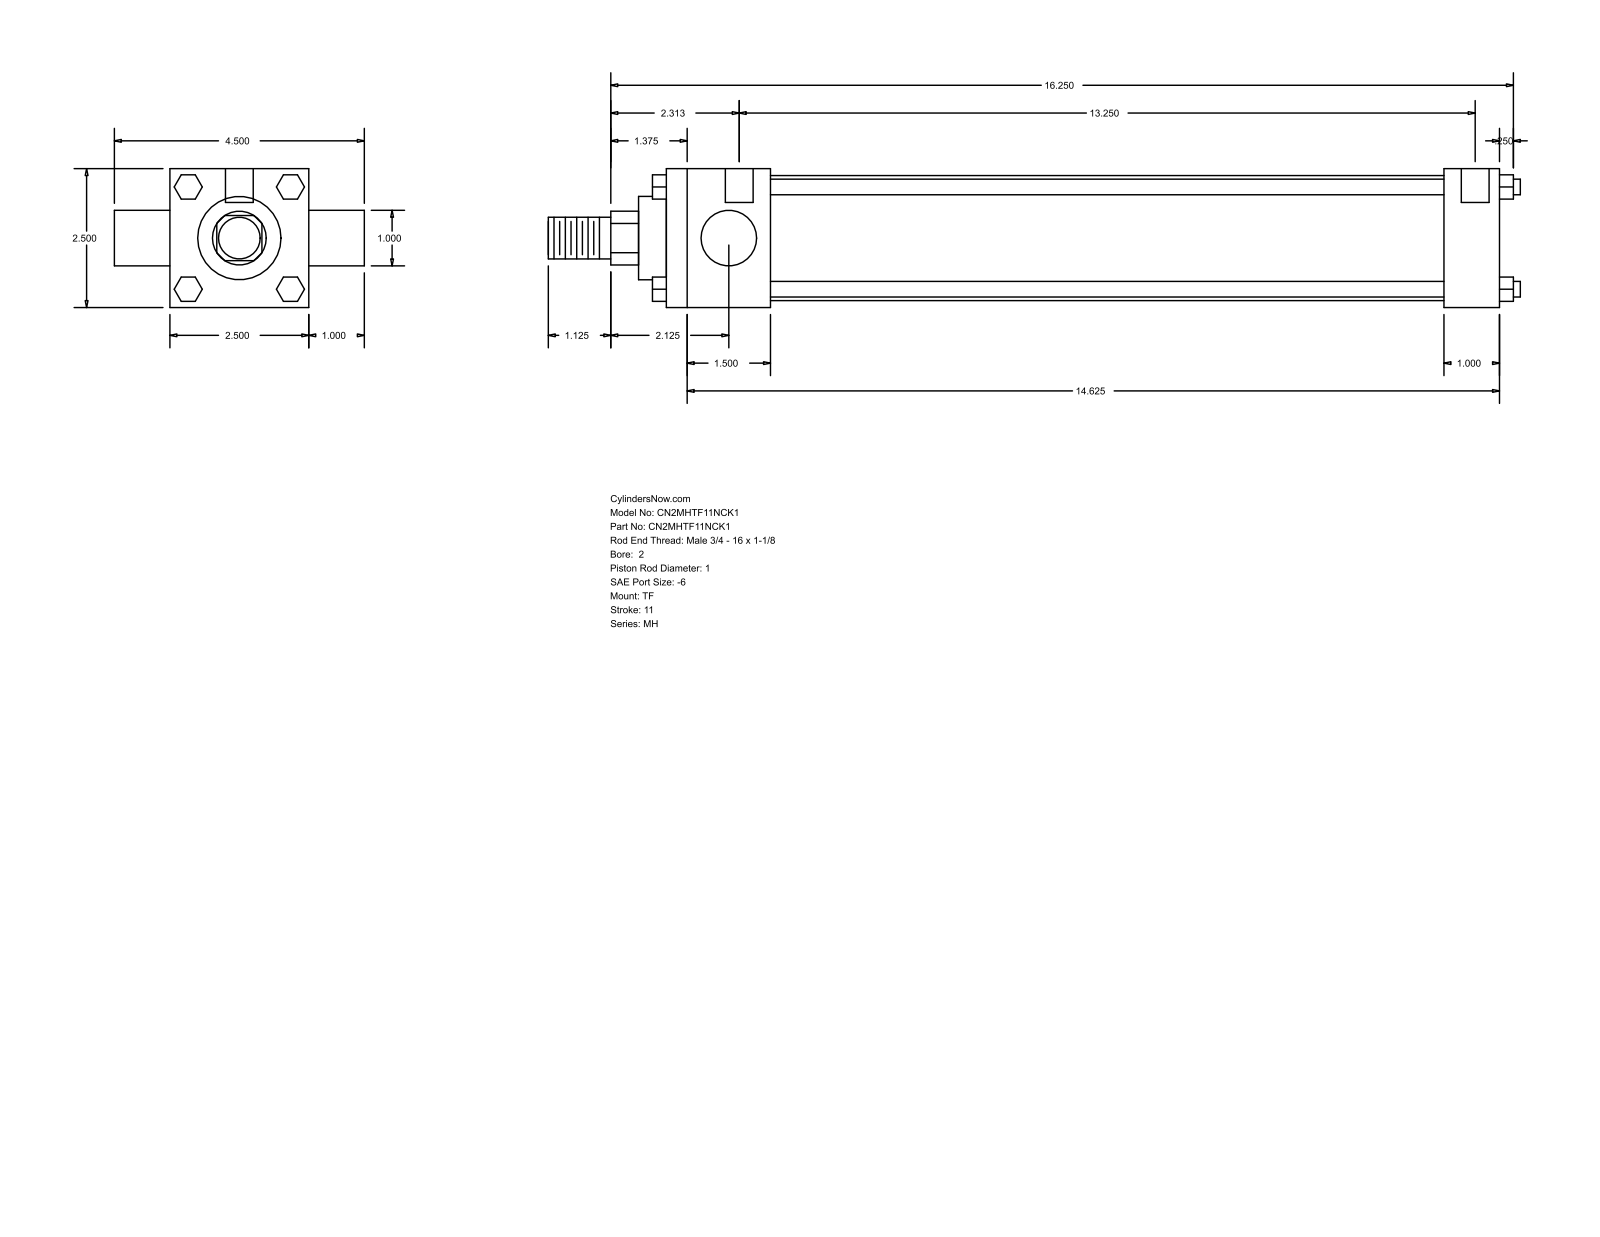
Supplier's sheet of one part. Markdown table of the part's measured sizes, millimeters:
| quantity | value |
| --- | --- |
| part name | MH_TF__0200_1 |
| STEP written by | GSSL Pune (CONFIG_CONTROL_DESIGN) |
| units | millimeters |
| bodies | 0 solids, 120 faces (92 planar, 28 cylindrical, 0 other) |
| overall size | 444.5 × 114.3 × 63.5 |
| round holes (diameter × count) | 5.56 × 3, 12.7 × 2 |
| round bosses / shafts (diameter × count) | 7.14 × 4, 25.4 × 2, 57.15 × 1, 38.1 × 1, 19.05 × 1 |
| partial cylindrical surfaces (radius × count) | 12.29 × 1 |
| main face-to-face distances | 63.5, 381, 25.4, 47.63, 355.6, 307.97, 333.37, 88.9, 393.7, 6.35 |
| hole center spacings | 3.17, 4.76, 336.55, 339.72, 341.31, 344.48 |
